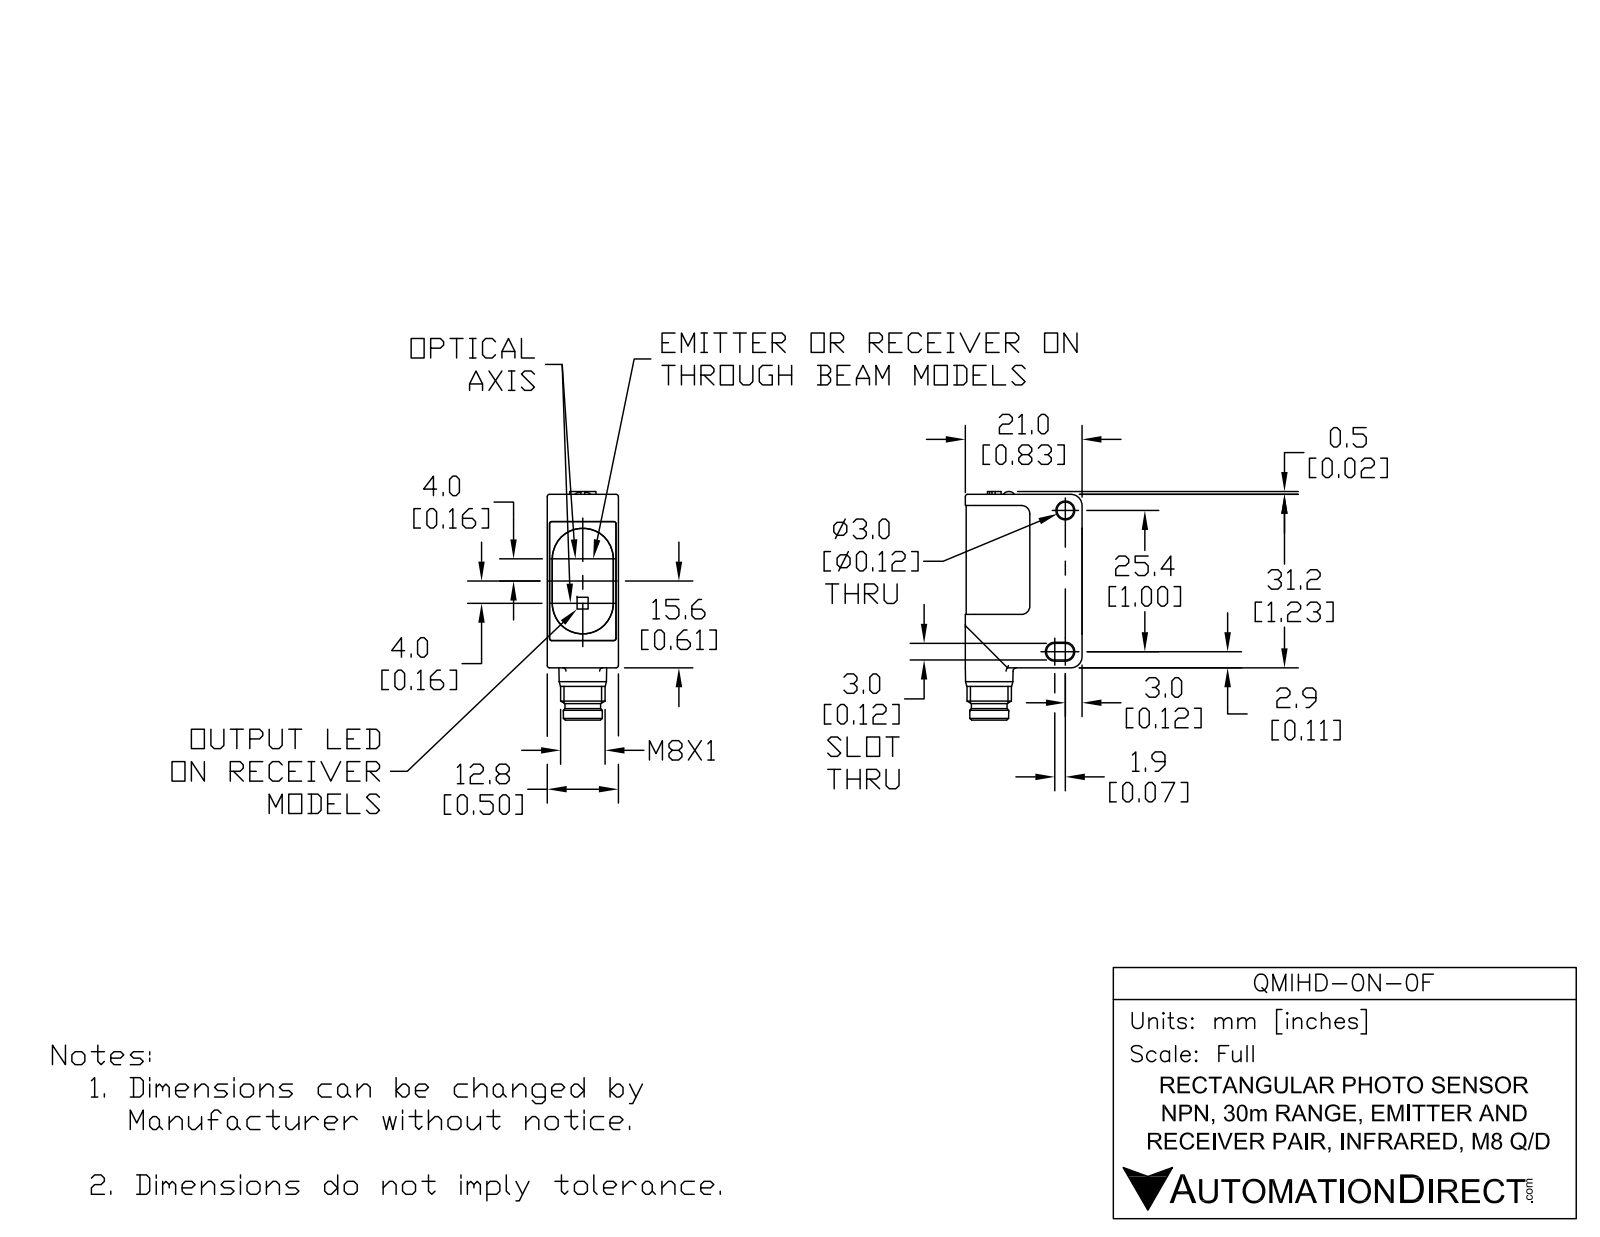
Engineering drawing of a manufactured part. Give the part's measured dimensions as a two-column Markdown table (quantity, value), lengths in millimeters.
| quantity | value |
| --- | --- |
| part name | QMIHD-0N-0F |
| STEP written by | SolidWorks 2017 (AUTOMOTIVE_DESIGN) |
| units | millimeters |
| bodies | 6 solids, 250 faces (114 planar, 89 cylindrical, 47 other) |
| overall size | 41.1 × 21 × 12.8 |
| volume | 7 750 mm³ |
| surface area | 4 974 mm² |
| round holes (diameter × count) | 3 × 2, 5.8 × 1 |
| round bosses / shafts (diameter × count) | 1 × 4, 8 × 1, 7 × 1, 6.4 × 1, 3.5 × 1 |
| partial cylindrical surfaces (radius × count) | 0.4 × 10, 1.5 × 6, 0.5 × 5, 0.6 × 4, 1 × 4, 1.7 × 2, 2 × 2, 5.5 × 2 |
| main face-to-face distances | 12.6, 0.5, 12.8, 2.8, 0.4, 12.5, 12.4, 12.2, 1.5, 18.1 |
| hole center spacings | 1 |
